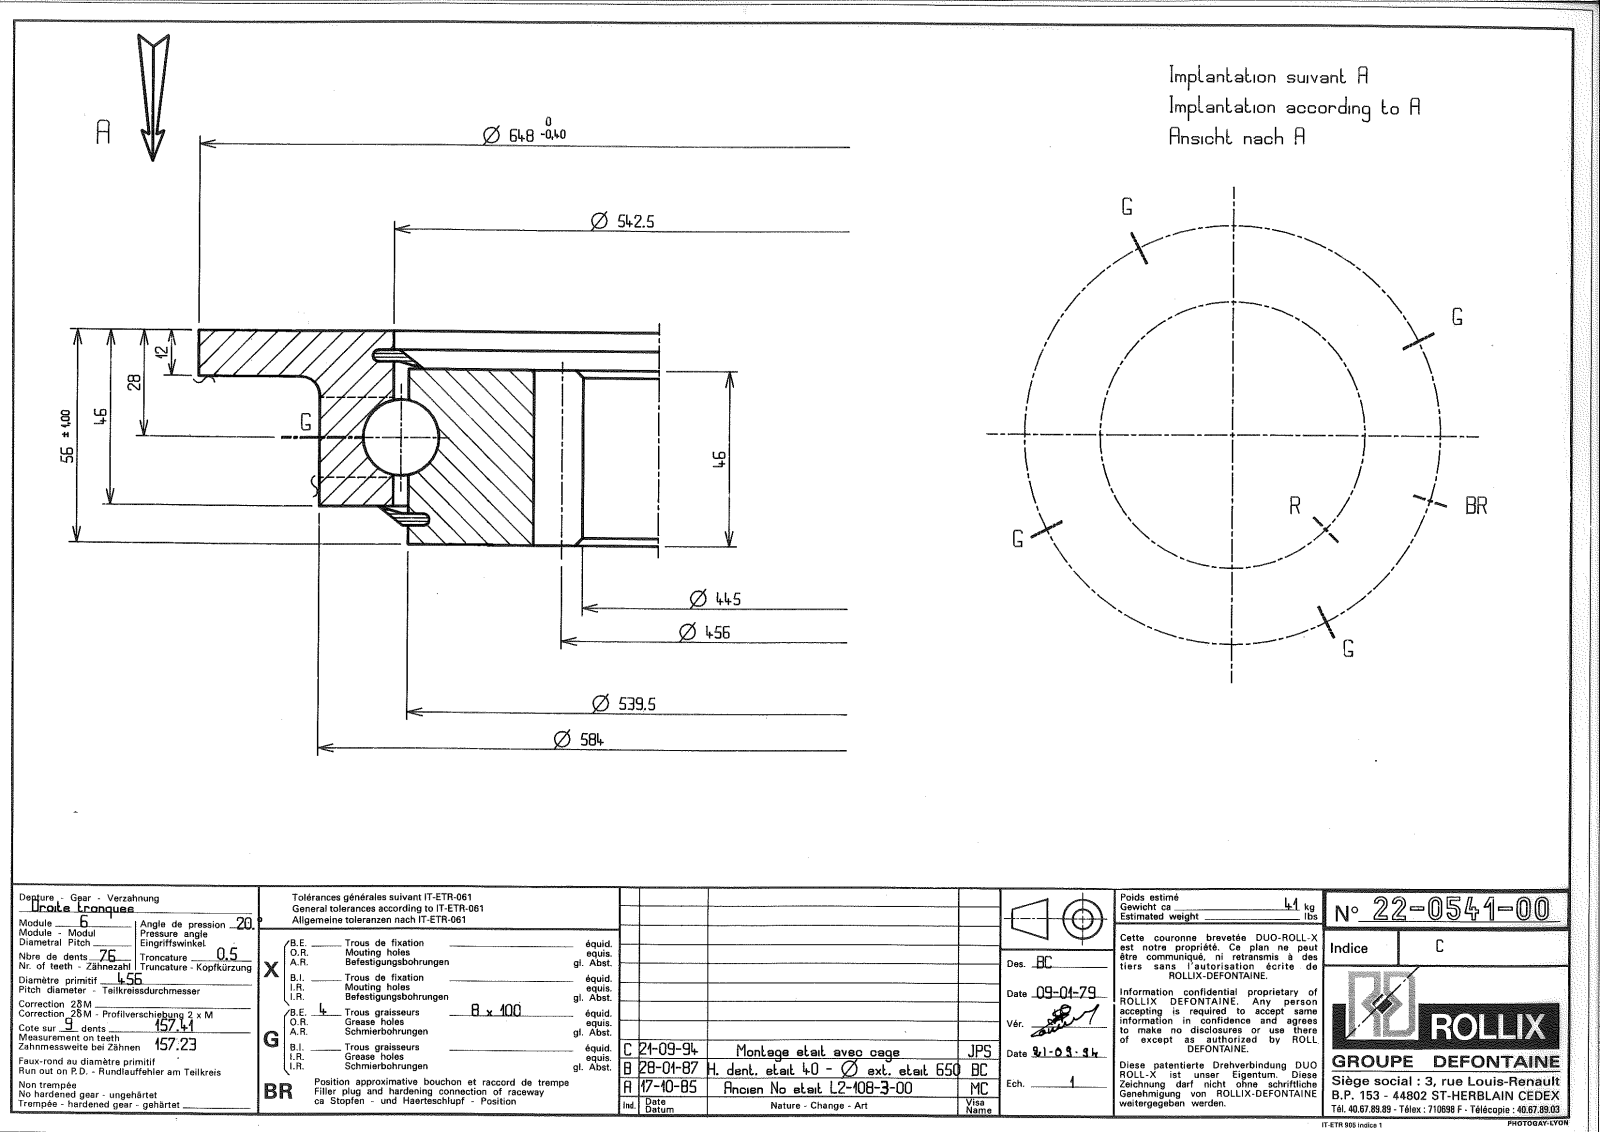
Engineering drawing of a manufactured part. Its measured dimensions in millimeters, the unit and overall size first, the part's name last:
Units: millimetres
Overall size (bounding box): 648 × 648 × 56
Round holes (diameter × count): ⌀7 ×4, ⌀545.5 ×1
Round bosses / shafts (diameter × count): ⌀8 ×4, ⌀648 ×1, ⌀584 ×1, ⌀536.5 ×1
Partial cylindrical surfaces — rounded edges, fillets, slot ends (radius × count): R222.5 ×1, R235.5 ×1
Main face-to-face distances: 10, 46, 56, 44, 2, 12, 34, 36, 8.05, 47.95
Volume: 4 869 000 mm³ · Surface area: 841 441 mm²
Bodies: 9 solids, 612 faces (205 planar, 185 cylindrical, 222 other)
Part name (STEP PRODUCT): 22-0541-00
STEP written by: SolidWorks 2016 (CONFIG_CONTROL_DESIGN)
